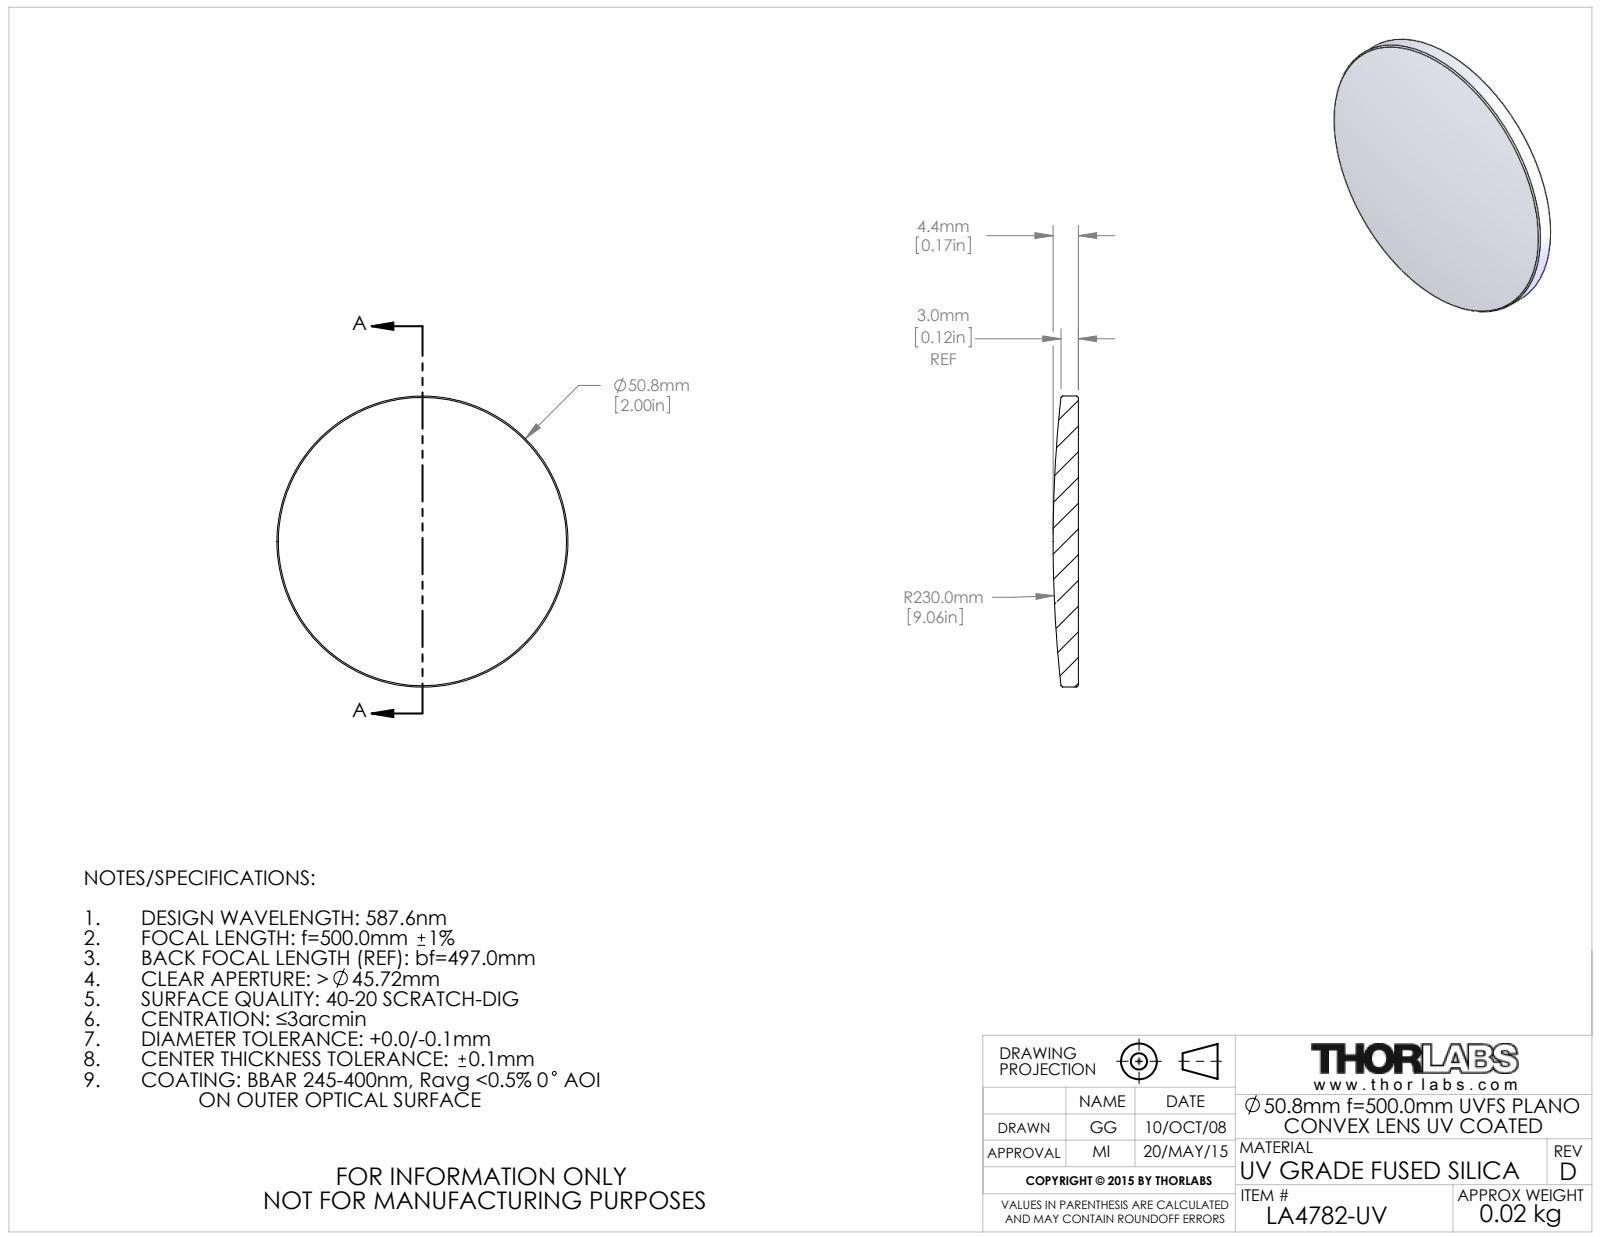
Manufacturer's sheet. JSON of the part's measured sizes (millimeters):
{"part_name": "4299-E0W", "step_written_by": "SolidWorks 2014 (CONFIG_CONTROL_DESIGN)", "units": "millimeters", "bodies": {"solids": 1, "faces": 9, "planar": 1, "cylindrical": 2, "other": 6}, "overall_size": [50.8, 50.8, 4.4], "volume_mm3": 7493, "surface_area_mm2": 4495, "round_bosses_or_shafts": [[50.8, 1]]}
